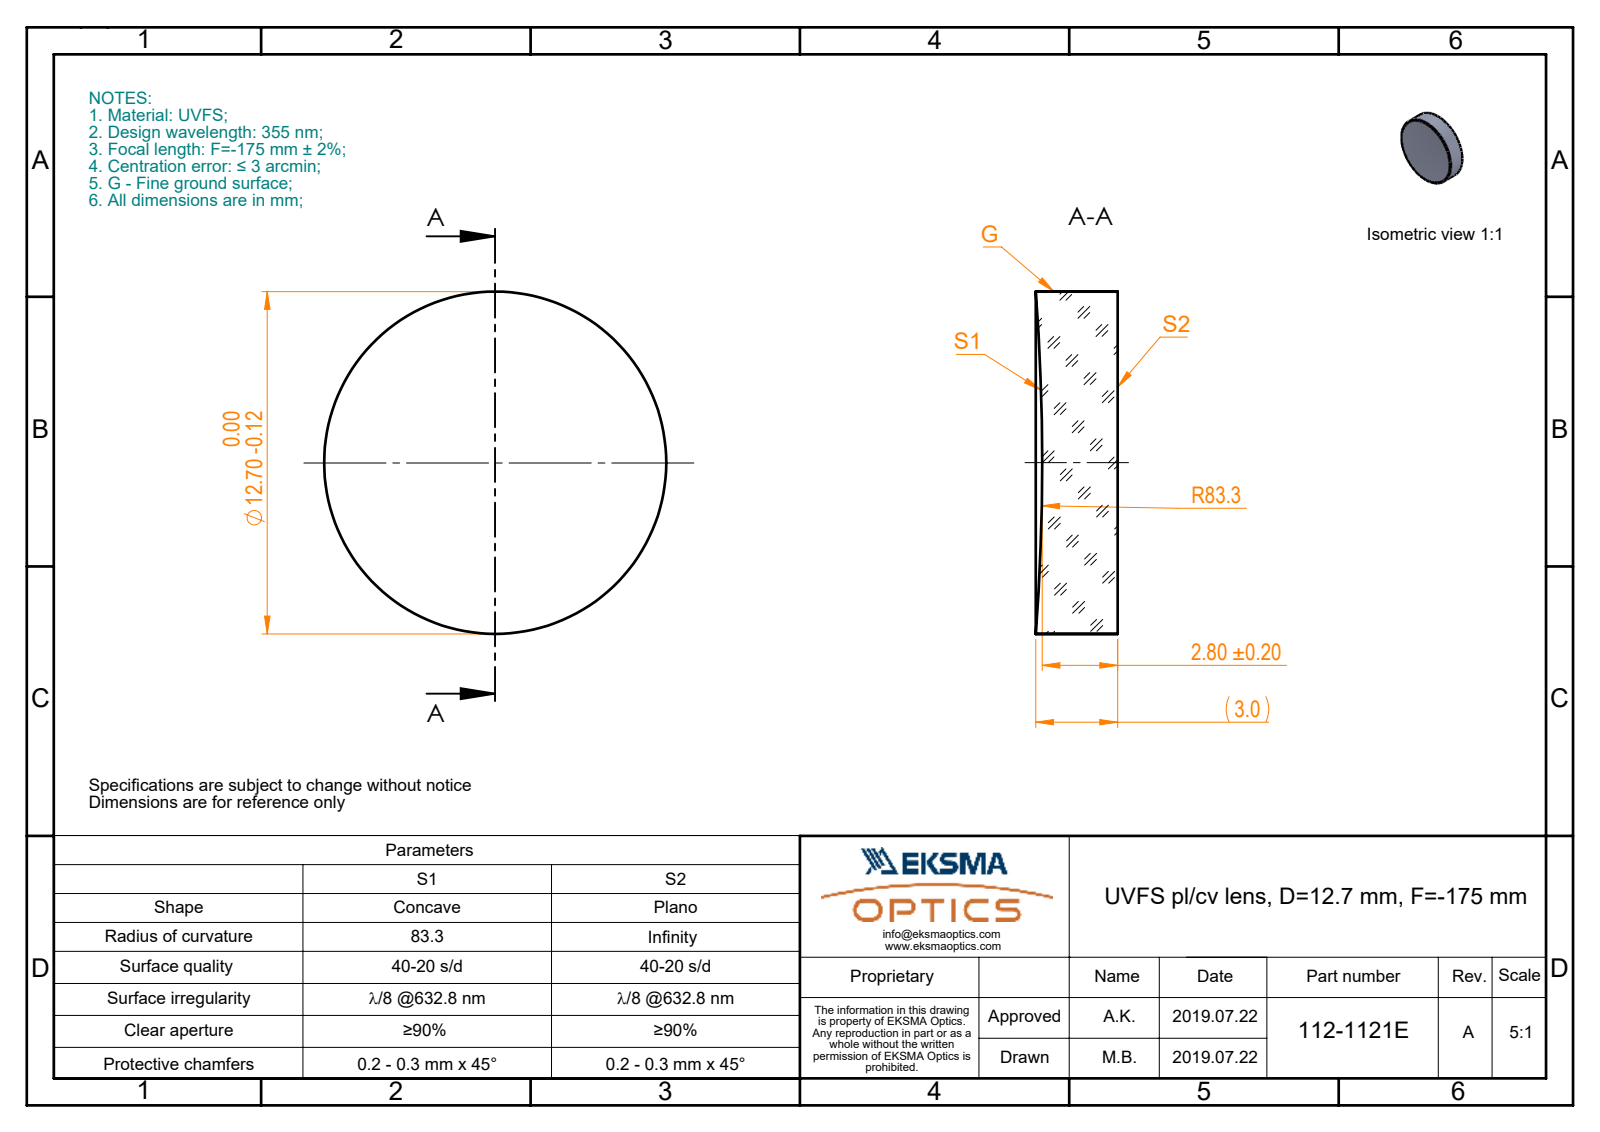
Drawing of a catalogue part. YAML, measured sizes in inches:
part_name: "112-1121E UVFS pl-cv 12.7 F-175"
step_written_by: "SolidWorks 2017 (CONFIG_CONTROL_DESIGN)"
units: inches
bodies: {solids: 1, faces: 5, planar: 1, cylindrical: 2, other: 2}
overall_size: [0.5, 0.5, 0.12]
volume: 0.023
surface_area: 0.581
round_bosses_or_shafts:
  - {diameter: 0.5, count: 1}
